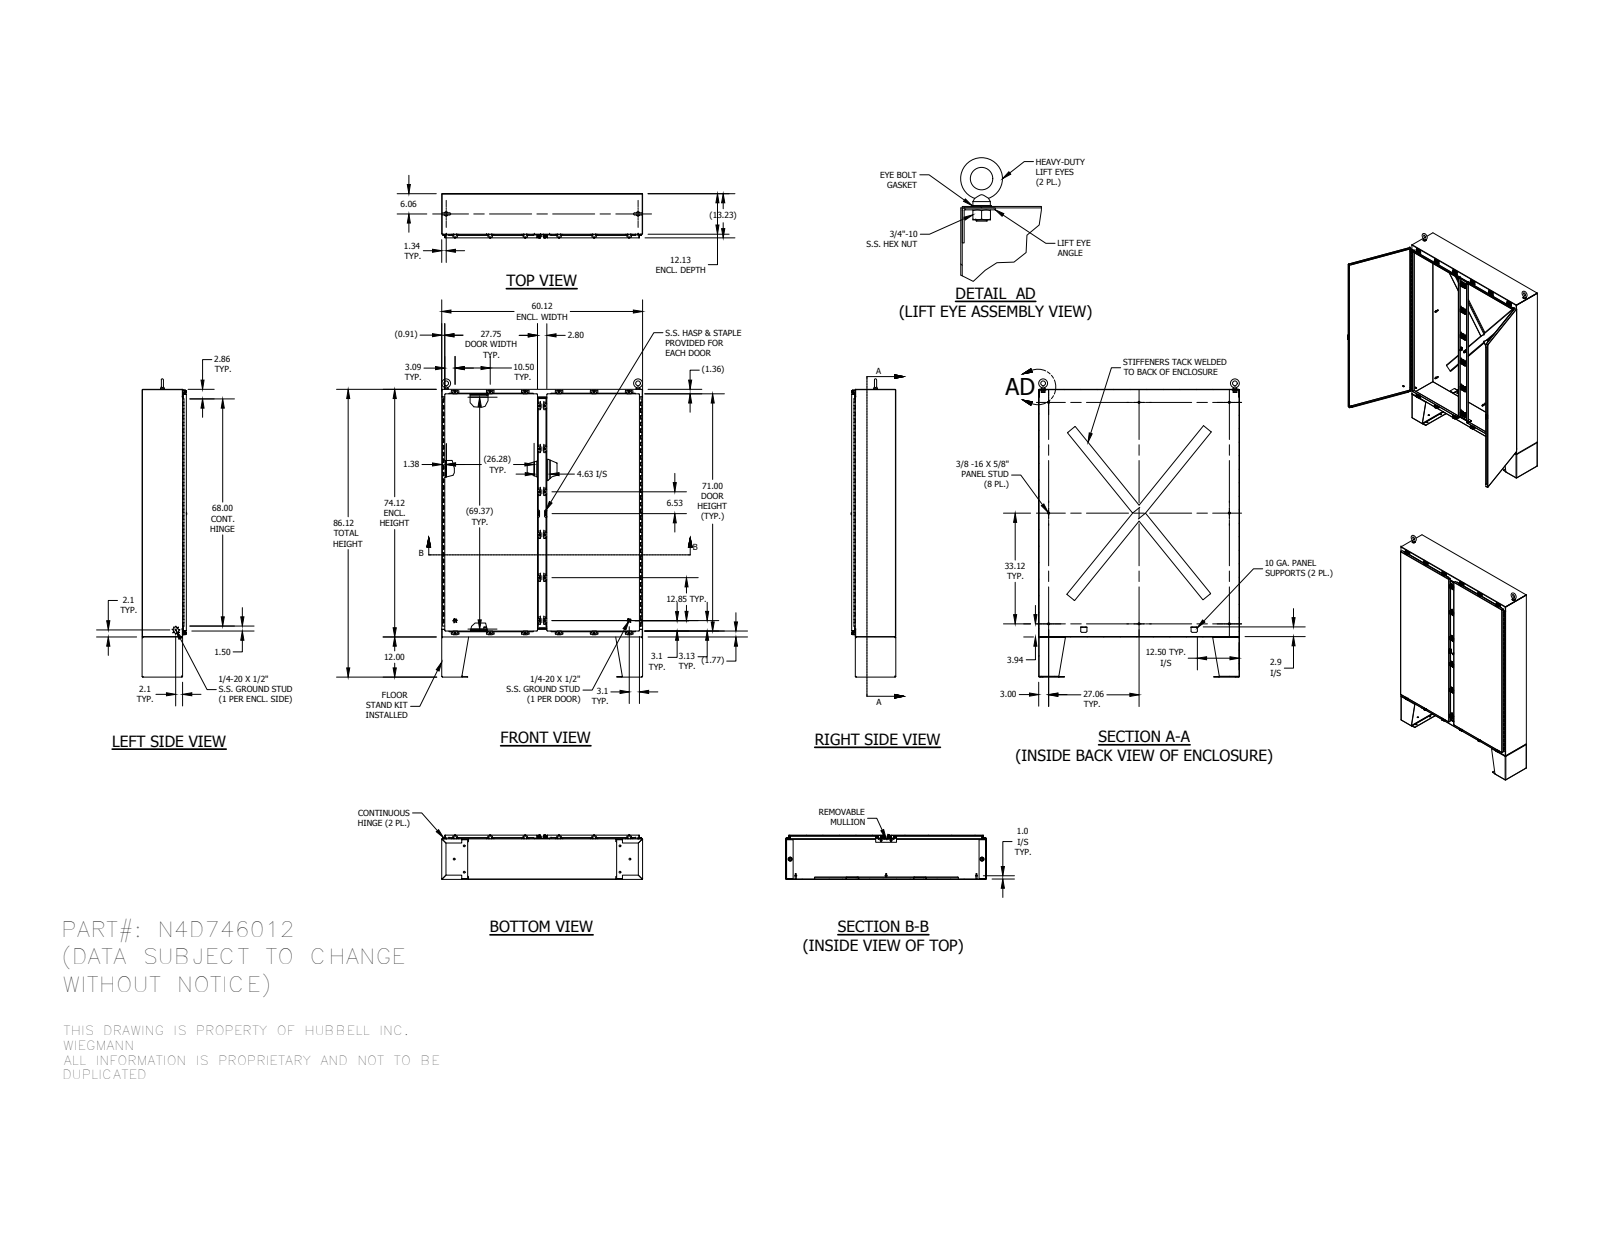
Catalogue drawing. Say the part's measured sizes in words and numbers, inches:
The part is named "N4D746012". Its 3-D file was written by "SolidWorks 2021 (AUTOMOTIVE_DESIGN)". It is 155 solids with 4852 faces: 2518 planar, 1874 cylindrical and 460 other. Overall it measures 89.248 by 60.125 by 13.355 inches. Its volume is 1 473 cubic inches and its surface area 30 926 square inches. Round holes: 48 of diameter 0.11, 24 of diameter 0.211, 24 of diameter 0.281, 18 of diameter 0.563, 16 of diameter 0.375, 4 of diameter 0.196, 4 of diameter 0.201, 4 of diameter 0.312, 4 of diameter 0.313, 2 of diameter 0.142, 2 of diameter 0.156, 2 of diameter 0.18. Round bosses or shafts: 27 of diameter 0.25, 24 of diameter 0.52, 24 of diameter 0.5, 24 of diameter 0.35, 10 of diameter 0.33, 6 of diameter 0.625, 3 of diameter 0.337, 2 of diameter 1.25. Partial cylindrical surfaces (rounded edges, fillets, slot ends): 268 of radius 0.03, 264 of radius 0.005, 56 of radius 0.125, 48 of radius 0.141, 36 of radius 0.25, 29 of radius 0.062, 24 of radius 0.033, 24 of radius 0.1. The main face-to-face distances are 0.094, 13.133, 13.039, 13.227, 60.031, 12.031, 1.102, 74.031, 0.125, 60.125. The hole center spacings are 10.5, 72.482, 0.876, 30.315, 1.625, 31.125, 31.939, 71.717.
